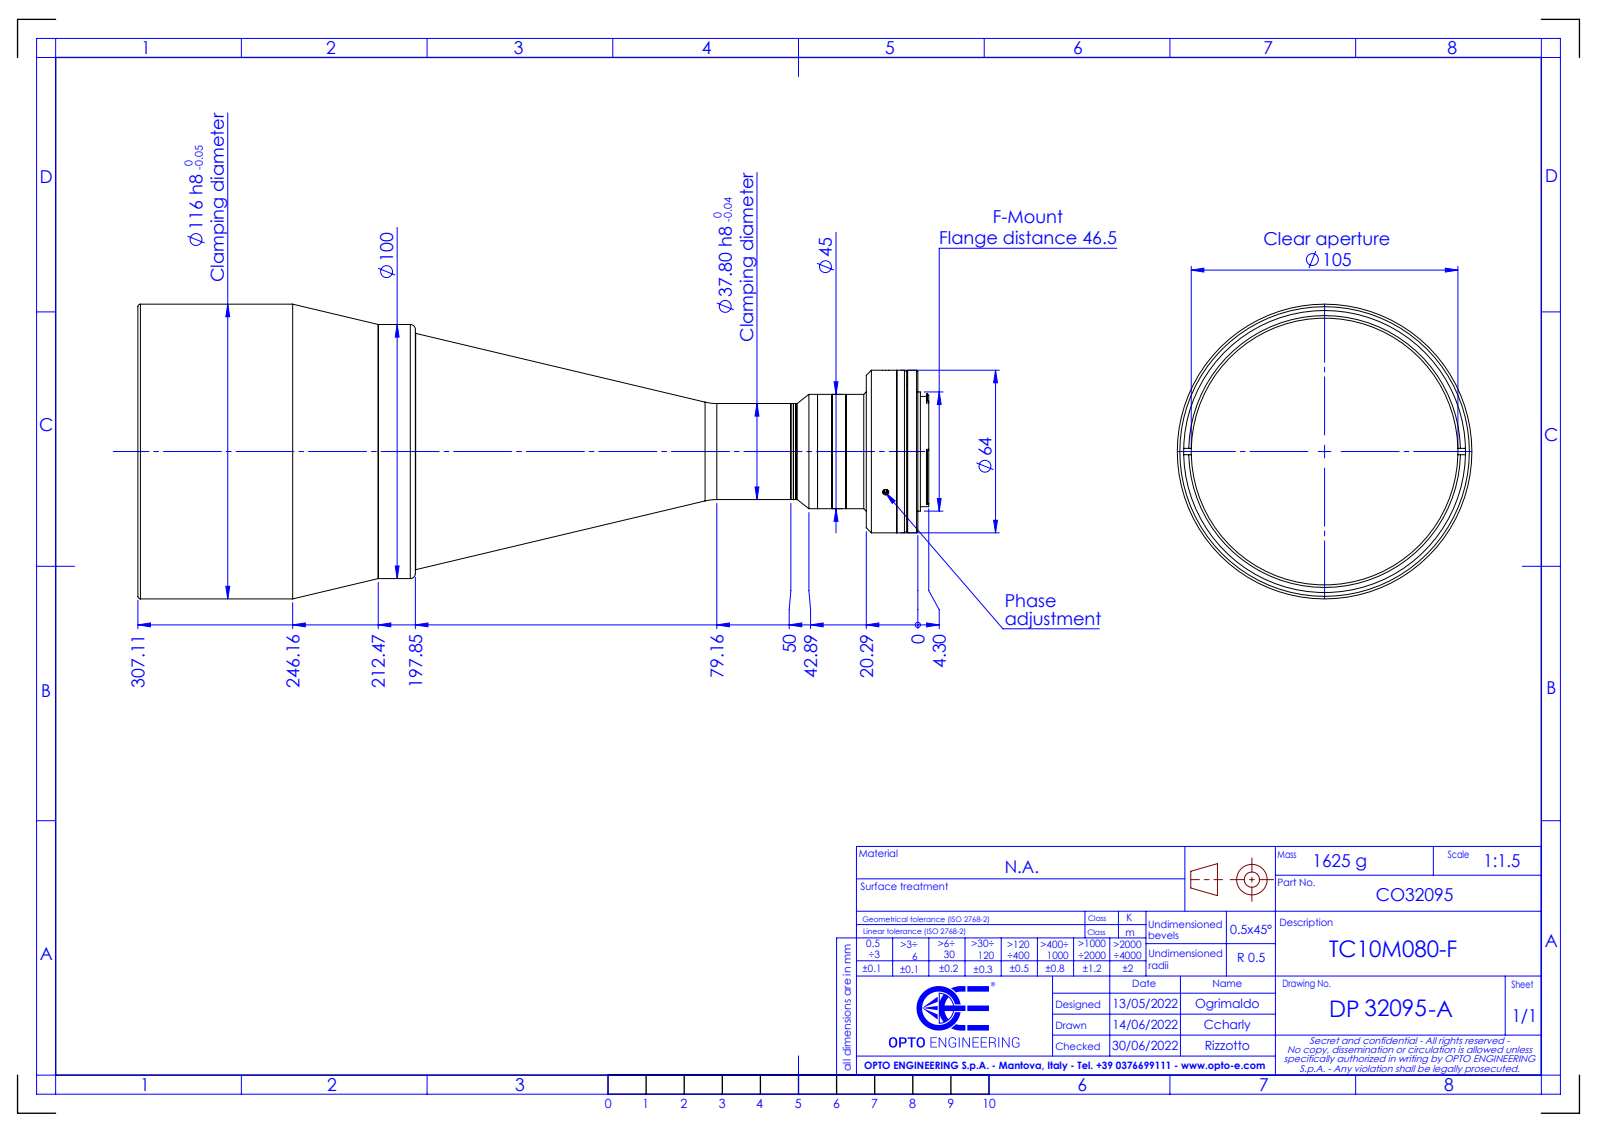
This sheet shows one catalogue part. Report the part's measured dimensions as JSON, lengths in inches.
{"part_name": "DP32095-A_TC10M080-F", "step_written_by": "SolidWorks 2021 (CONFIG_CONTROL_DESIGN)", "units": "inches", "bodies": {"solids": 0, "faces": 127, "planar": 37, "cylindrical": 60, "other": 30}, "overall_size": [12.26, 4.567, 4.567], "round_holes": [[0.098, 3], [1.299, 1], [1.654, 1], [4.134, 1], [4.37, 1]], "round_bosses_or_shafts": [[4.567, 1], [3.937, 1], [3.661, 1], [2.52, 1], [2.5, 1], [1.846, 1], [1.772, 1], [1.709, 1]], "partial_cylinders_radius": [[0.02, 3], [0.045, 2], [0.892, 1]], "face_to_face_distances": [0.208, 0.039, 0.591, 0.799, 11.27, 11.862, 12.07, 11.912, 0.642, 0.05]}
